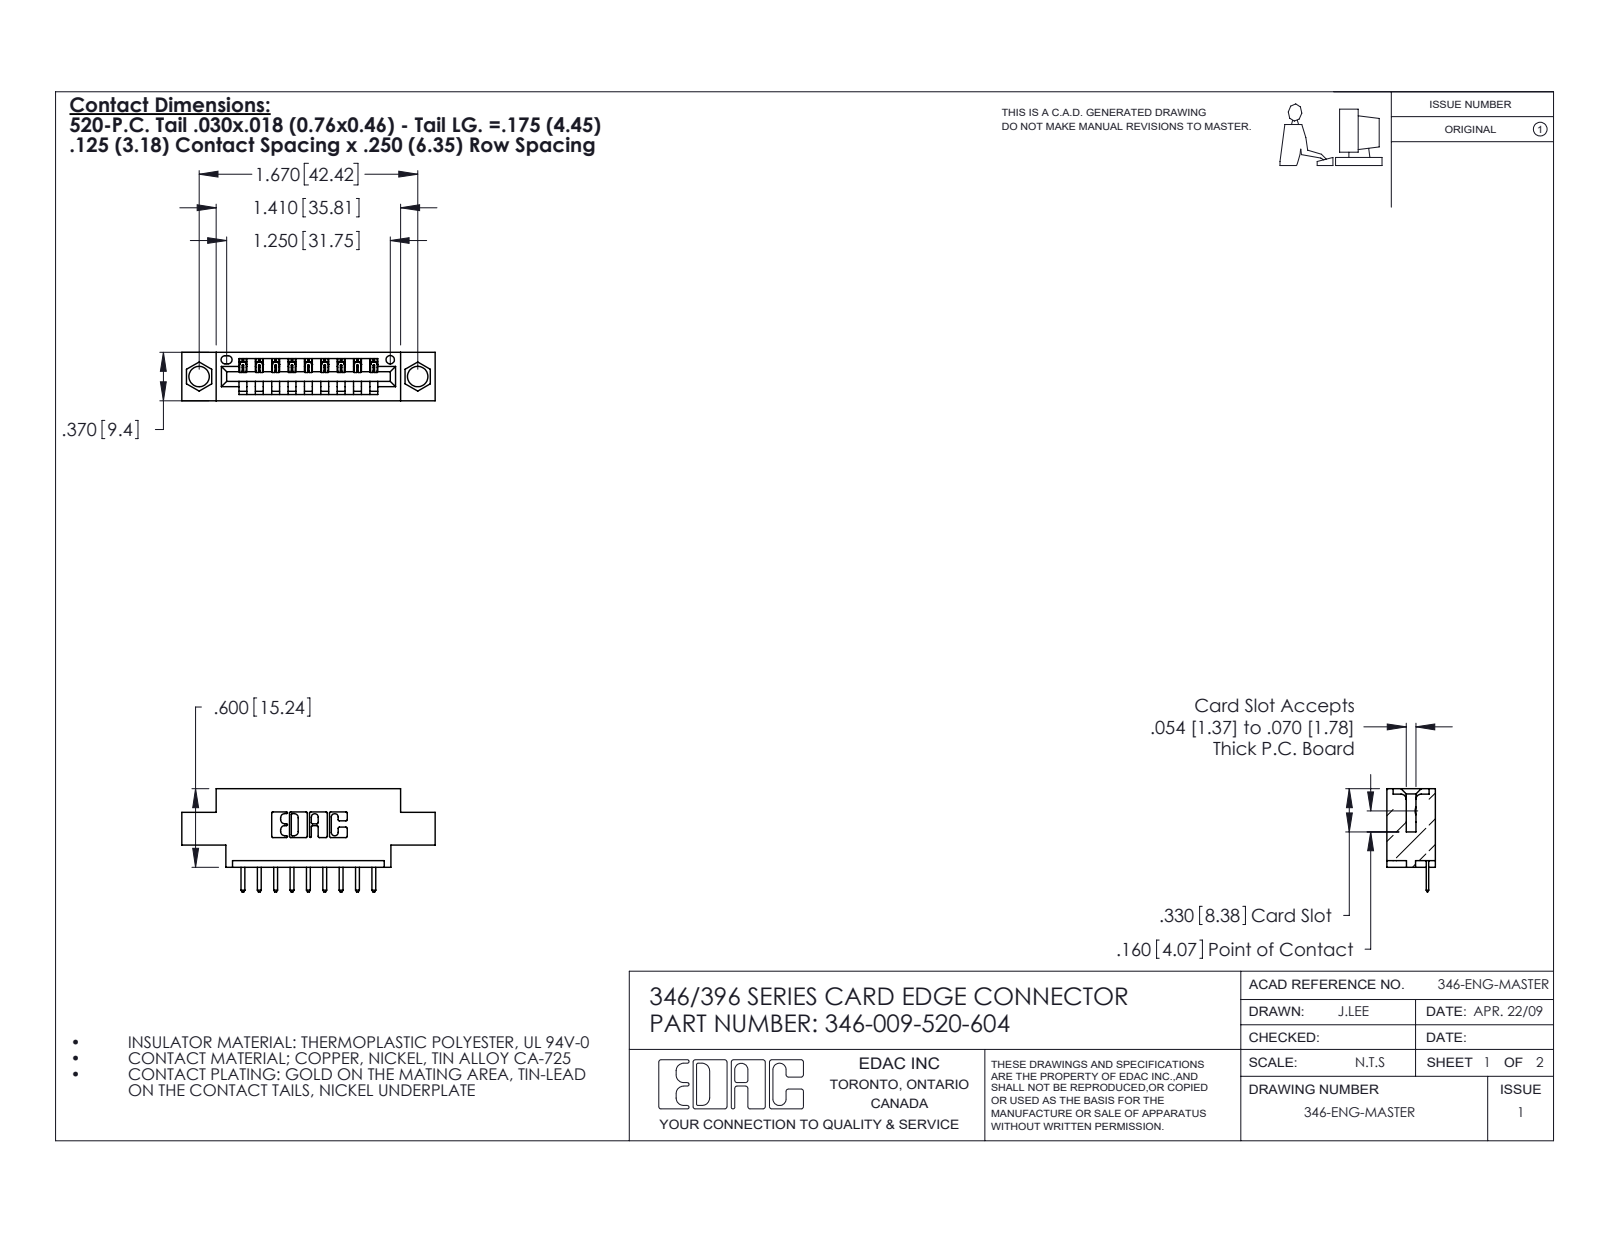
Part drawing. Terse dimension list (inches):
name: 345-292-001_345-293-120; 346-009-520-604; 346 Part_0.170 Offset - 0.156 Dia-TH
written by: SolidWorks 2020 (CONFIG_CONTROL_DESIGN)
unit: in
bodies: 10 solids, 698 faces (472 planar, 226 cylindrical, 0 other)
size: 1.935 × 0.788 × 0.37
volume: 0.256 in³; area: 7.429 in²
holes: 2× ⌀0.156, 1× ⌀0.064
rounds: 22× R0.01, 20× R0.01, 18× R0.006, 6× R0.007, 6× R0.031, 3× R0.026, 2× R0.031, 2× R0.04
face distances: 0.25, 0.37, 0.048, 0.322, 0.222, 0.148, 0.1, 0.174, 0.072, 0.298
hole spacings: 0.246, 1.465, 1.67
